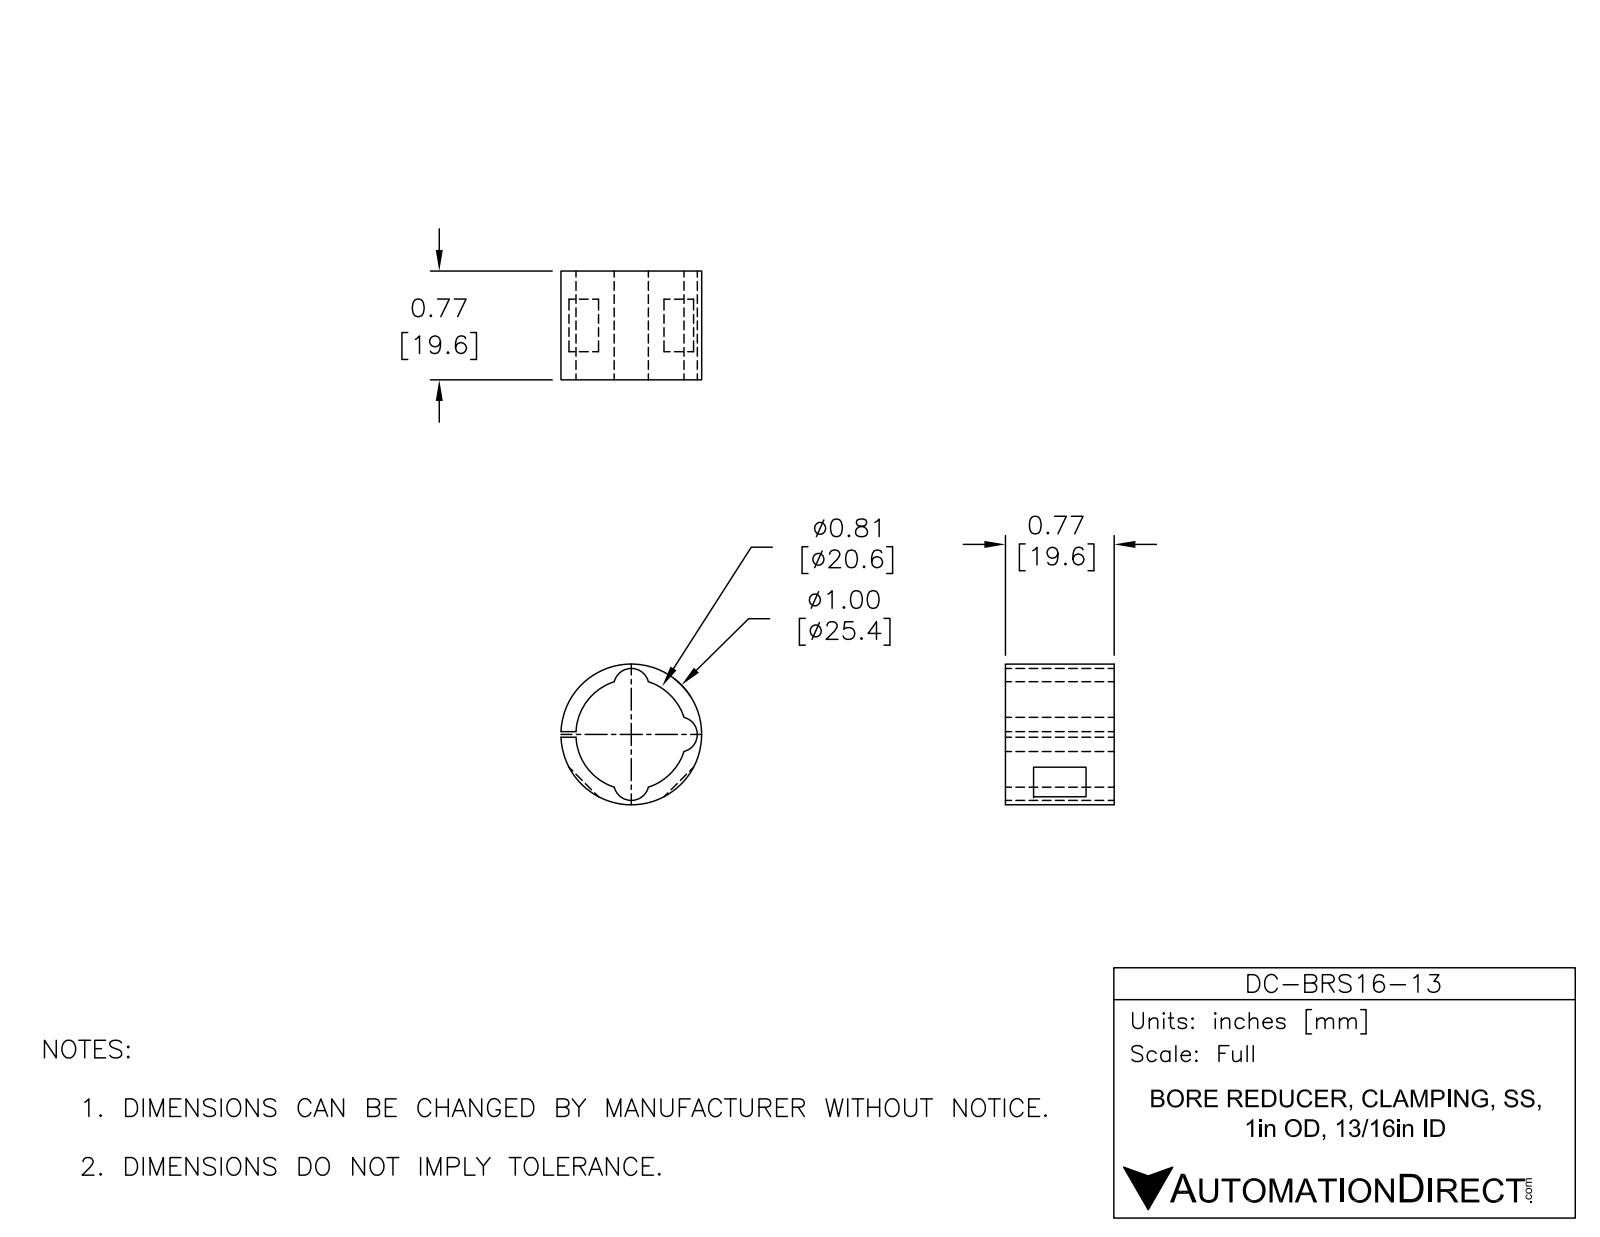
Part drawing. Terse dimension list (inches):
name: DC-BRS16-13
written by: SolidWorks 2015 (AUTOMOTIVE_DESIGN)
unit: in
bodies: 1 solid, 21 faces (10 planar, 11 cylindrical, 0 other)
size: 1 × 1 × 0.773
volume: 0.127 in³; area: 4.993 in²
bosses: 1× ⌀1
rounds: 3× R0.125, 1× R0.437
face distances: 0.773, 0.04, 0.2, 0.573, 0.373
